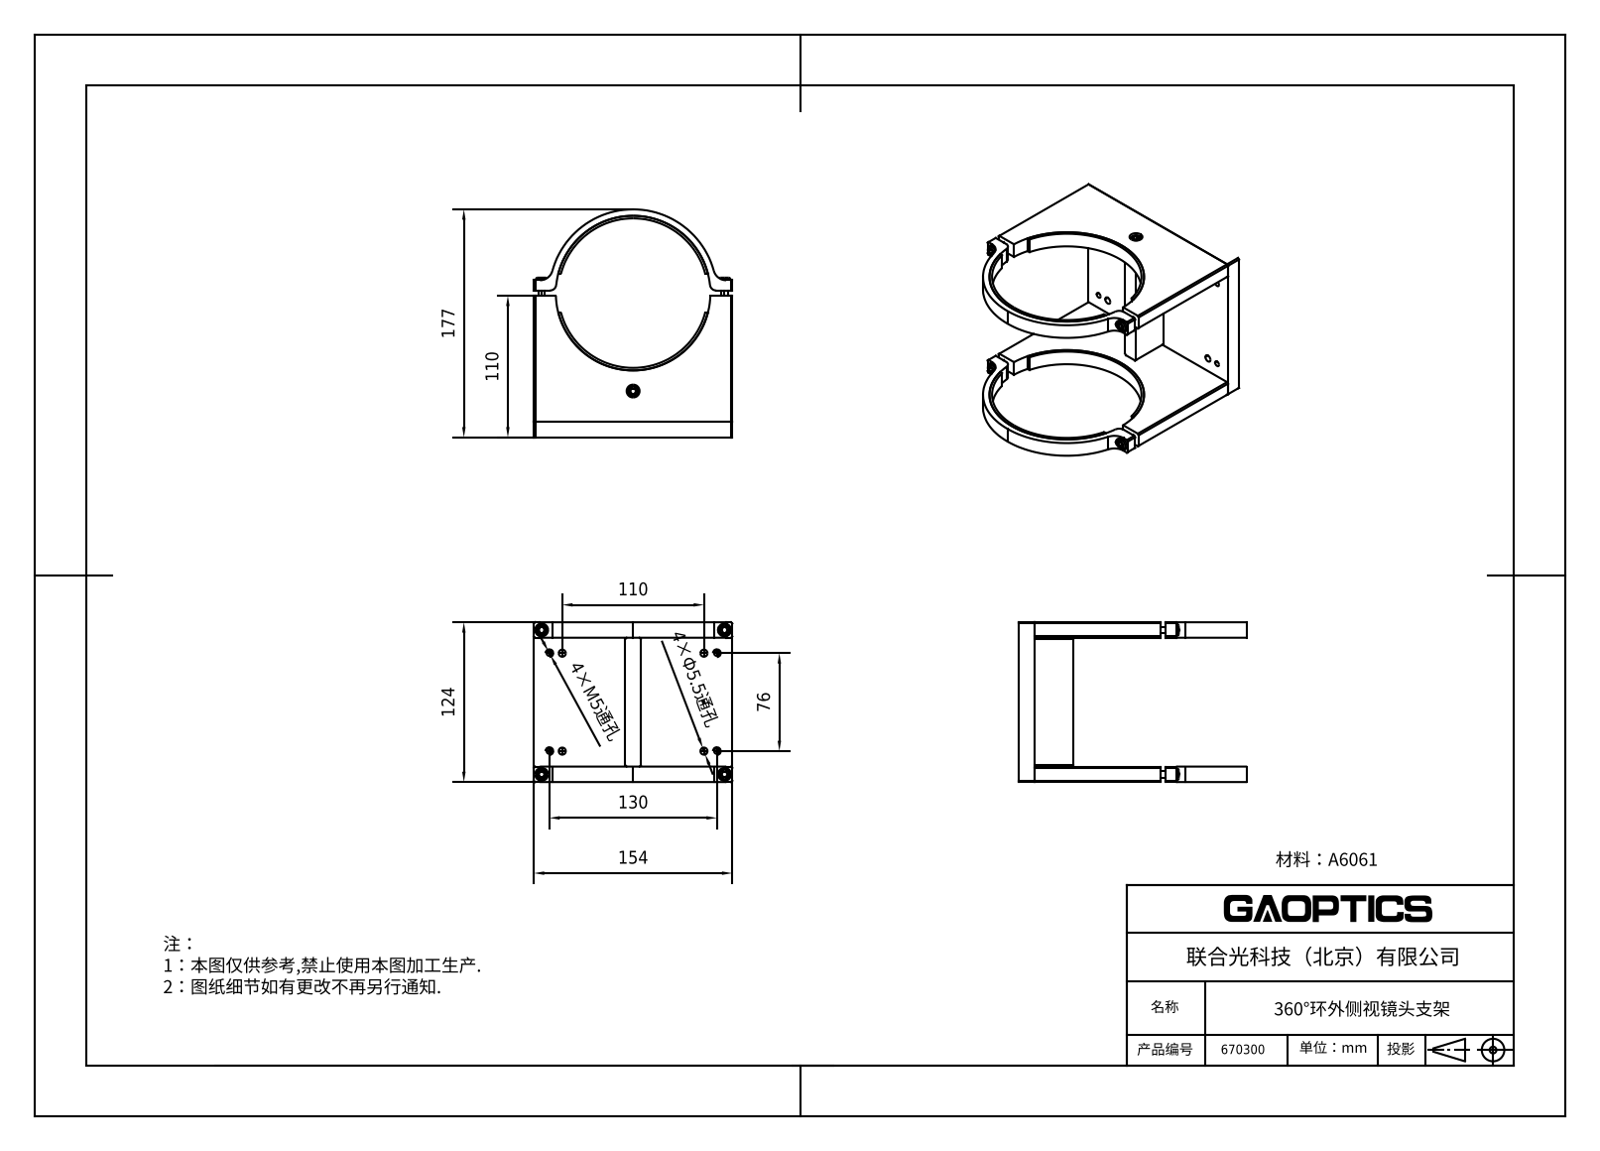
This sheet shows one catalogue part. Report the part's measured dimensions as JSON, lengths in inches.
{"part_name": "203.stp.IGS; M5X12.stp.IGS; 360支架1.IGS; 204.stp.IGS (+4 more)", "step_written_by": "SolidWorks 2019 (AUTOMOTIVE_DESIGN)", "units": "inches", "bodies": {"solids": 22, "faces": 420, "planar": 0, "cylindrical": 0, "other": 420}, "overall_size": [6.969, 6.063, 4.882], "volume_in3": 32.67, "surface_area_in2": 232.1}
